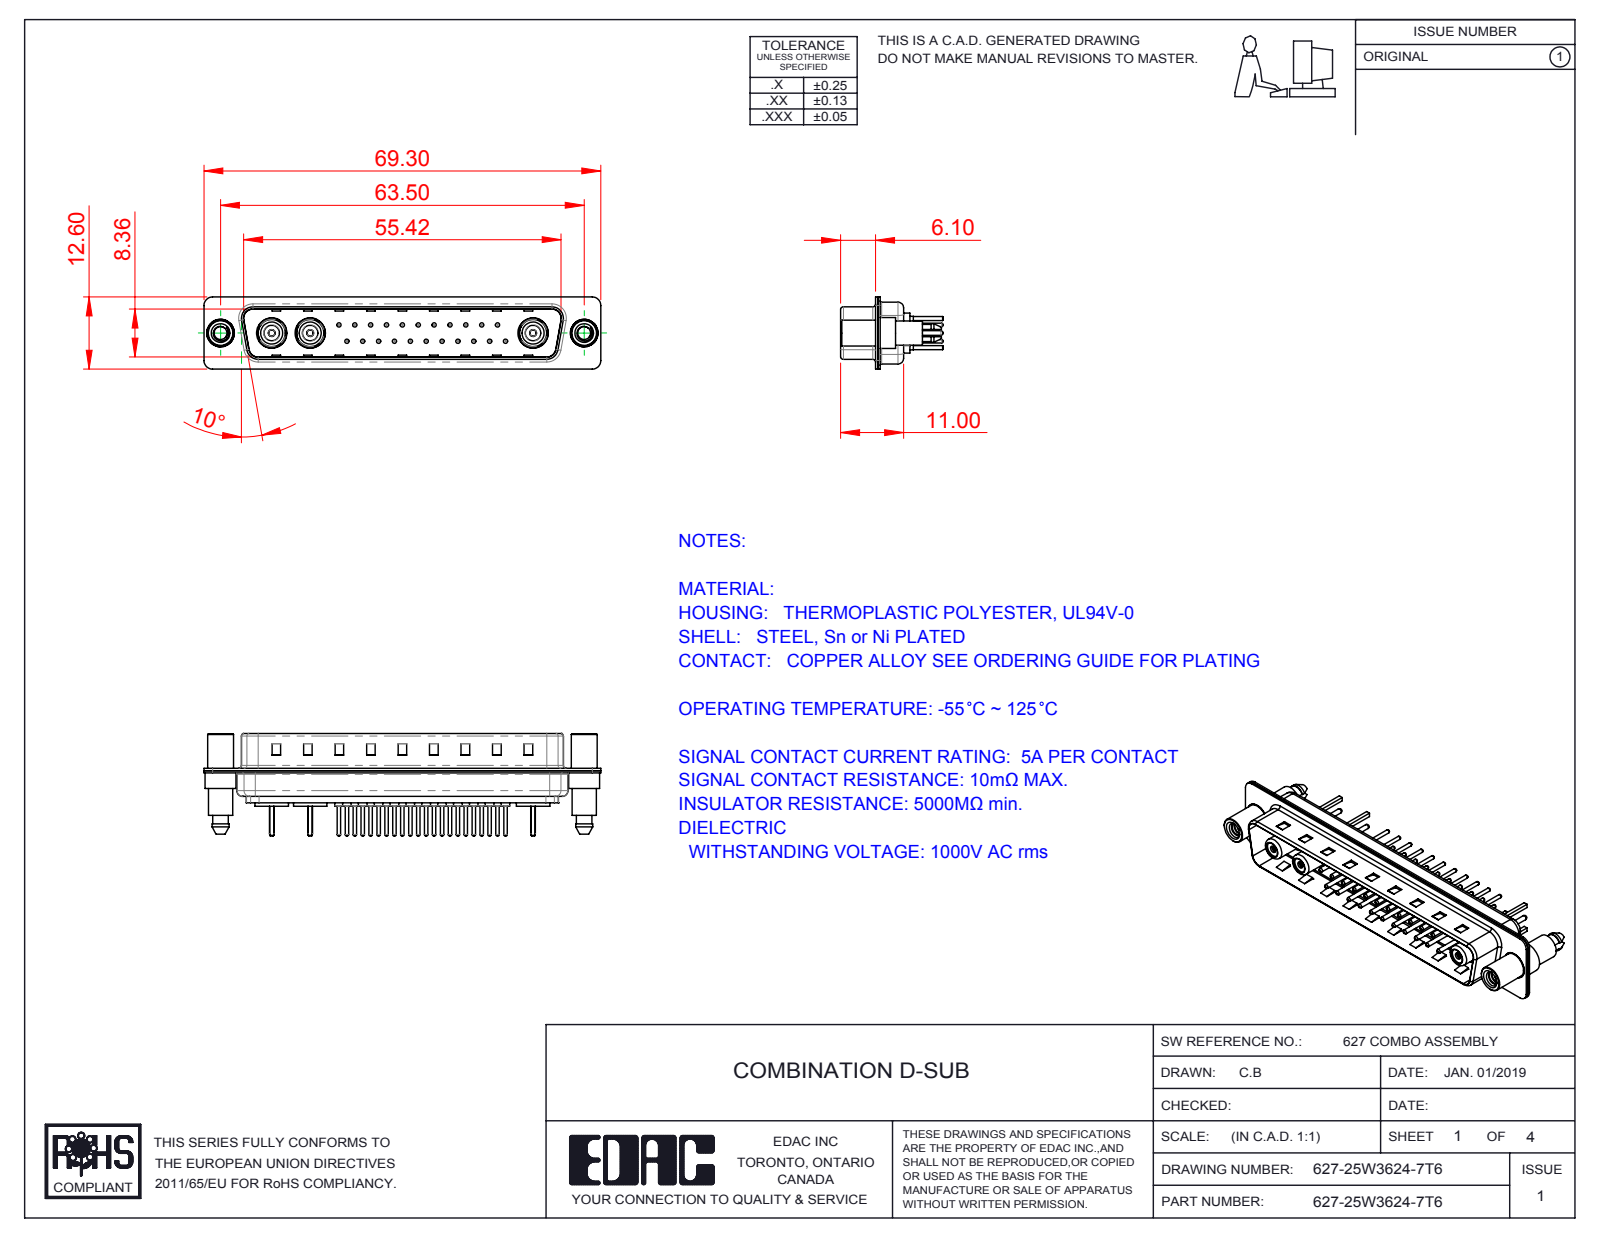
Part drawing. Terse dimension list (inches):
name: 627Combo Housing_25W3; Co-Ax Jack_Straight PC Tail; 627Combo Shell Front_37 Contacts; 627Combo Threaded Standoff and Boardlock_6 (+8 more)
written by: SolidWorks 2016 (CONFIG_CONTROL_DESIGN)
unit: in
bodies: 42 solids, 1611 faces (516 planar, 618 cylindrical, 477 other)
size: 2.728 × 0.705 × 0.496
volume: 0.254 in³; area: 16.84 in²
holes: 25× ⌀0.063, 22× ⌀0.03, 22× ⌀0.079, 3× ⌀0.043, 3× ⌀0.047, 3× ⌀0.059, 3× ⌀0.098, 3× ⌀0.106, 3× ⌀0.134, 3× ⌀0.191, 3× ⌀0.209, 2× ⌀0.089
bosses: 22× ⌀0.059, 22× ⌀0.024, 3× ⌀0.23, 3× ⌀0.205, 3× ⌀0.189, 3× ⌀0.186, 3× ⌀0.152, 3× ⌀0.148
rounds: 18× R0.059, 12× R0.079, 10× R0.063, 8× R0.02, 4× R0.01, 4× R0.024, 4× R0.026, 4× R0.035
face distances: 0.016, 0.032, 0.377, 0.345, 0.059, 0.048, 0.22, 0.017, 0.393, 0.361
hole spacings: 0.124, 0.109, 0.218, 0.327, 0.198, 0.198, 0.295, 0.436
